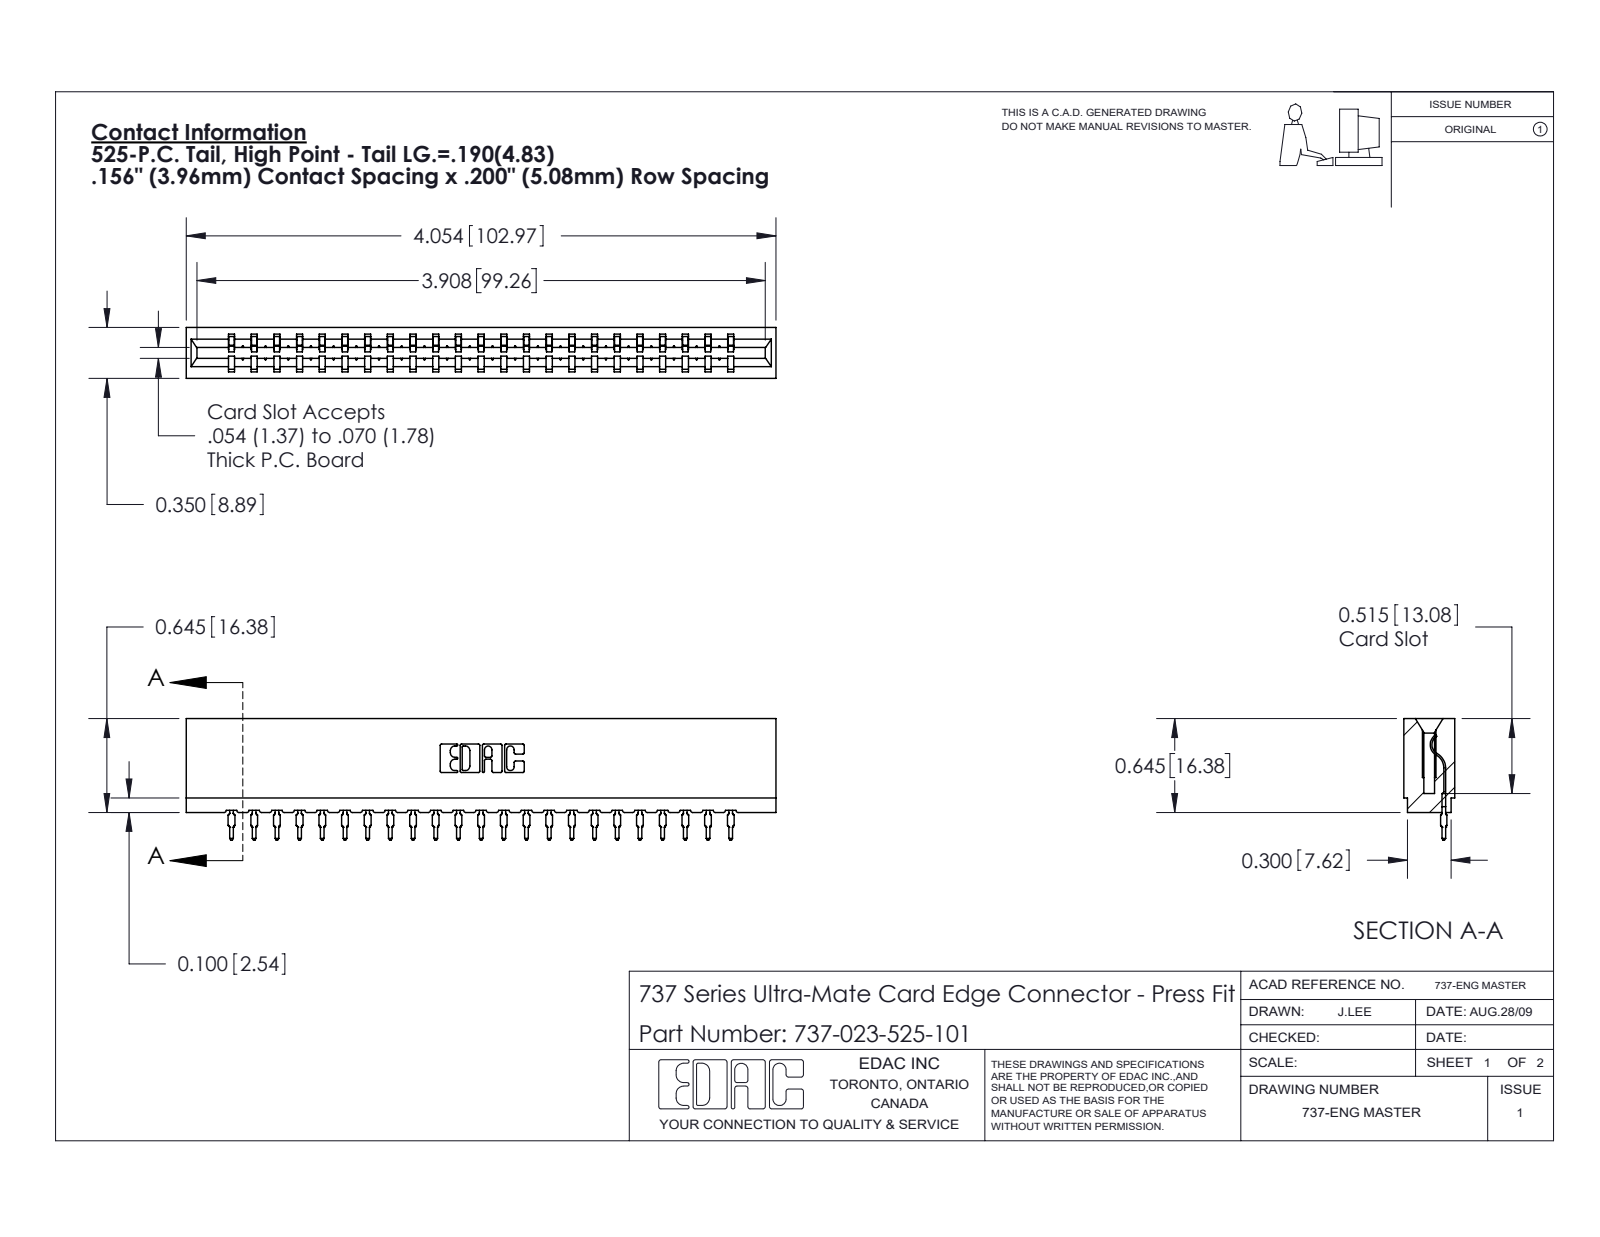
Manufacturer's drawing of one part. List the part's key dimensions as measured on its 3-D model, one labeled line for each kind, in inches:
Part name (STEP PRODUCT): 745-292-001_525; 737 Part_Insulator Option - 01; 737-023-525-101
STEP written by: SolidWorks 2020 (CONFIG_CONTROL_DESIGN)
Units: inches
Bodies: 24 solids, 2693 faces (1618 planar, 477 cylindrical, 598 other)
Overall size (bounding box): 4.054 × 0.836 × 0.35
Volume: 0.614 in³ · Surface area: 20.32 in²
Partial cylindrical surfaces — rounded edges, fillets, slot ends (radius × count): R0.015 ×46, R0.021 ×46, R0.01 ×22, R0.007 ×6, R0.031 ×6, R0.005 ×4, R0.011 ×4, R0.026 ×3
Main face-to-face distances: 0.138, 0.212, 0.35, 0.156, 0.624, 0.074, 0.045, 0.305, 0.093, 0.167
